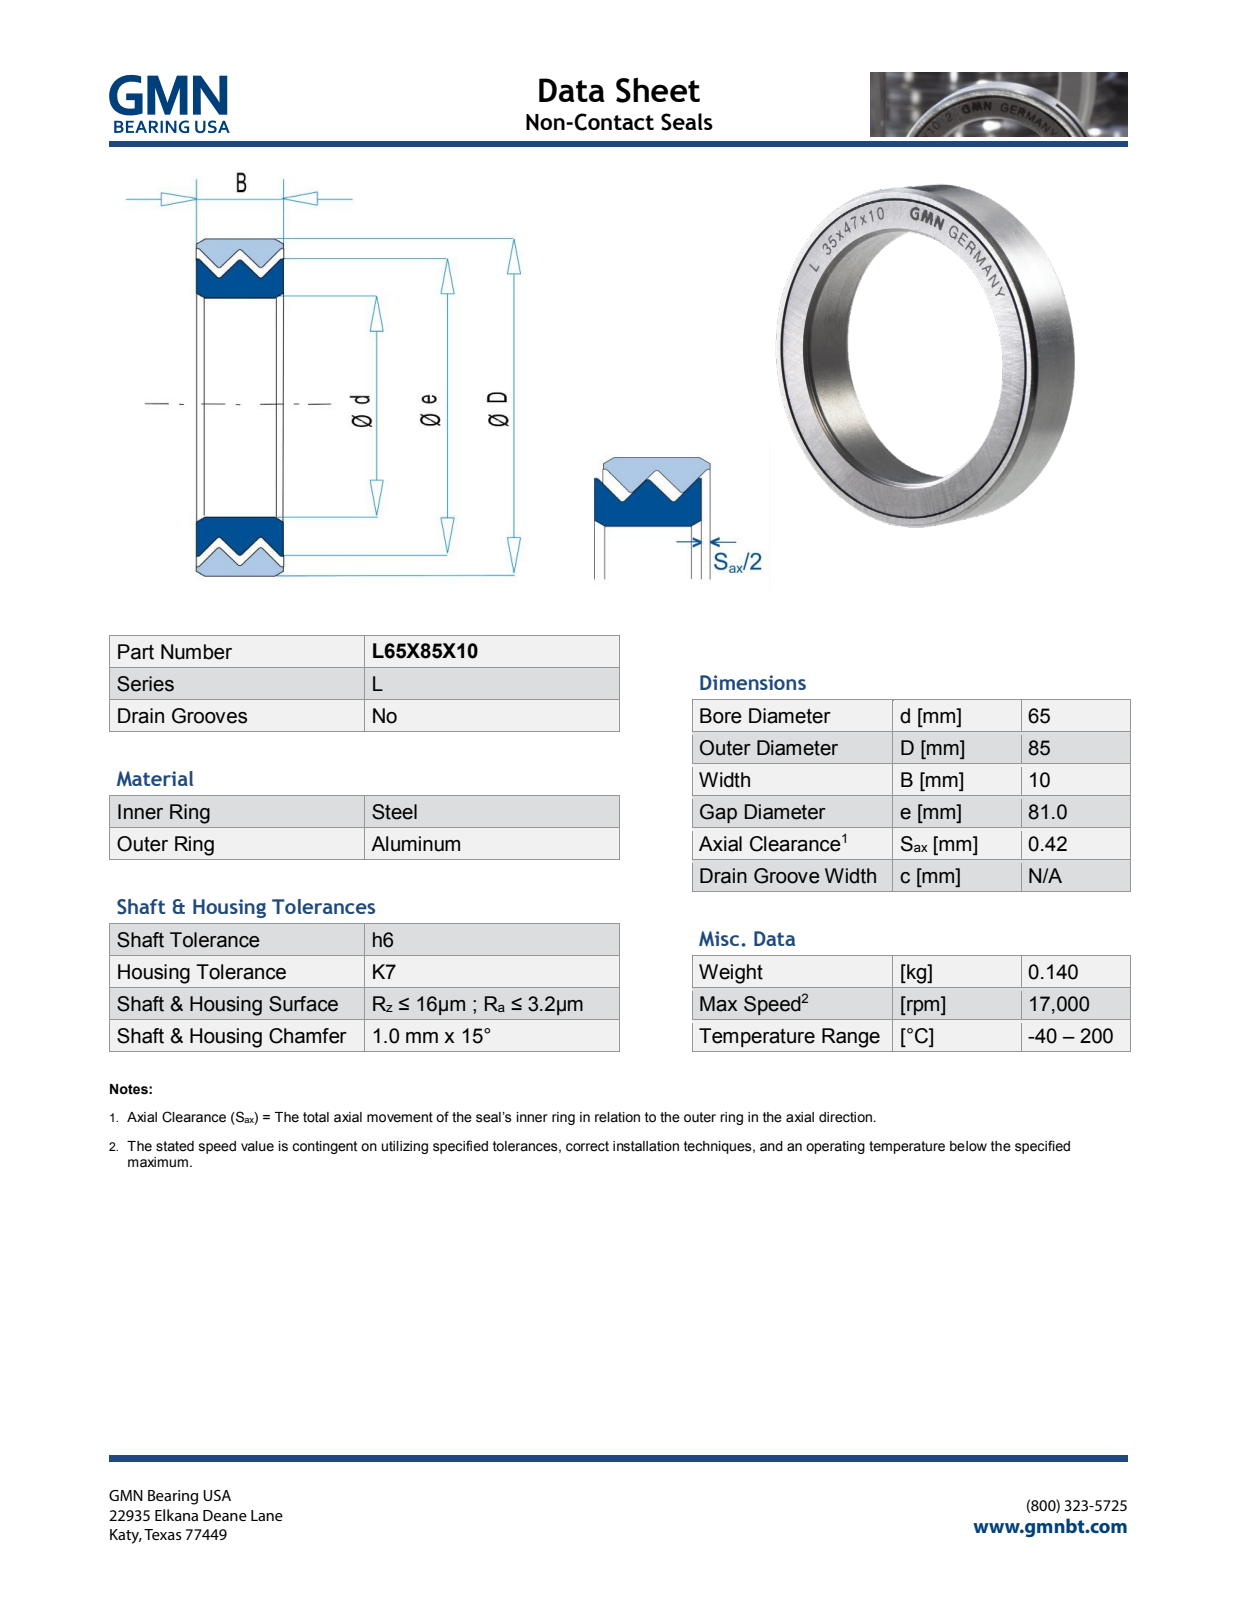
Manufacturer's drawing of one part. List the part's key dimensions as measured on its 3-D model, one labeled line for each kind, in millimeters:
Part name (STEP PRODUCT): L65X85X10_PRT
STEP written by: PRO/ENGINEER BY PARAMETRIC TECHNOLOGY CORPORATION, 2013150 (AUTOMOTIVE_DESIGN)
Units: millimetres
Bodies: 2 solids, 634 faces (578 planar, 12 cylindrical, 44 other)
Overall size (bounding box): 85 × 85 × 10.07
Volume: 22 811 mm³ · Surface area: 15 630 mm²
Round holes (diameter × count): ⌀65 ×1, ⌀81.3 ×1
Round bosses / shafts (diameter × count): ⌀85 ×1, ⌀81 ×1
Main face-to-face distances: 10, 10.07, 0.68, 5.42, 0.69, 3.84, 0.57, 5.43, 4.74, 4.75
